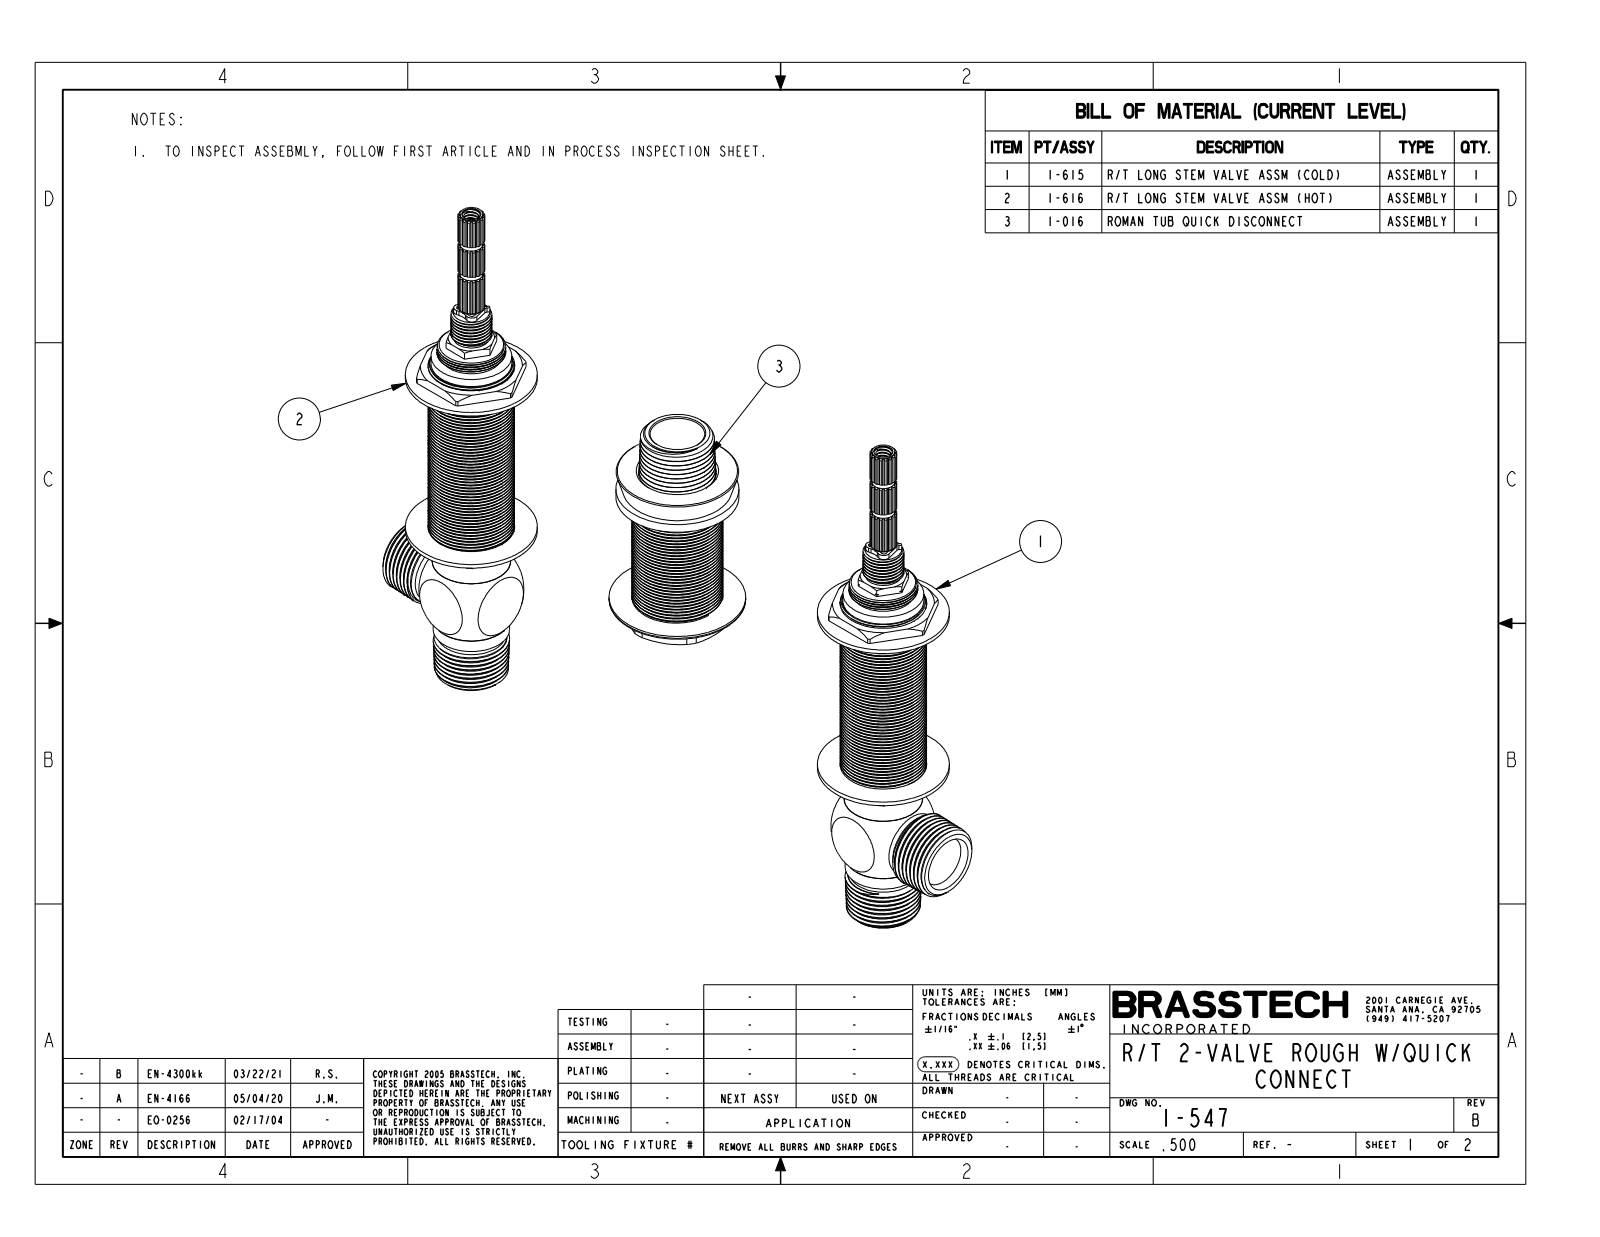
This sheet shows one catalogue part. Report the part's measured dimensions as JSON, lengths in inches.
{"part_name": "1-547", "step_written_by": "CREO PARAMETRIC BY PTC INC, 2018400 (AUTOMOTIVE_DESIGN)", "units": "inches", "bodies": {"solids": 3, "faces": 1463, "planar": 340, "cylindrical": 642, "other": 481}, "overall_size": [10.52, 7.701, 1.875], "volume_in3": 16.78, "surface_area_in2": 121.3, "round_holes": [[0.201, 2], [0.709, 1]], "round_bosses_or_shafts": [[1.811, 2], [1.187, 2], [1.11, 2], [1.075, 2], [1.047, 2], [0.945, 2], [0.929, 2], [0.835, 2]], "partial_cylinders_radius": [[0.04, 8], [0.08, 8], [0.164, 2], [0.185, 2], [0.26, 2], [0.3, 2], [0.775, 2], [0.758, 1]], "face_to_face_distances": [0.061, 2.561, 2.5, 2.622, 0.146, 0.207, 2.707, 2.768, 0.873, 0.812], "hole_center_spacings": [8]}
